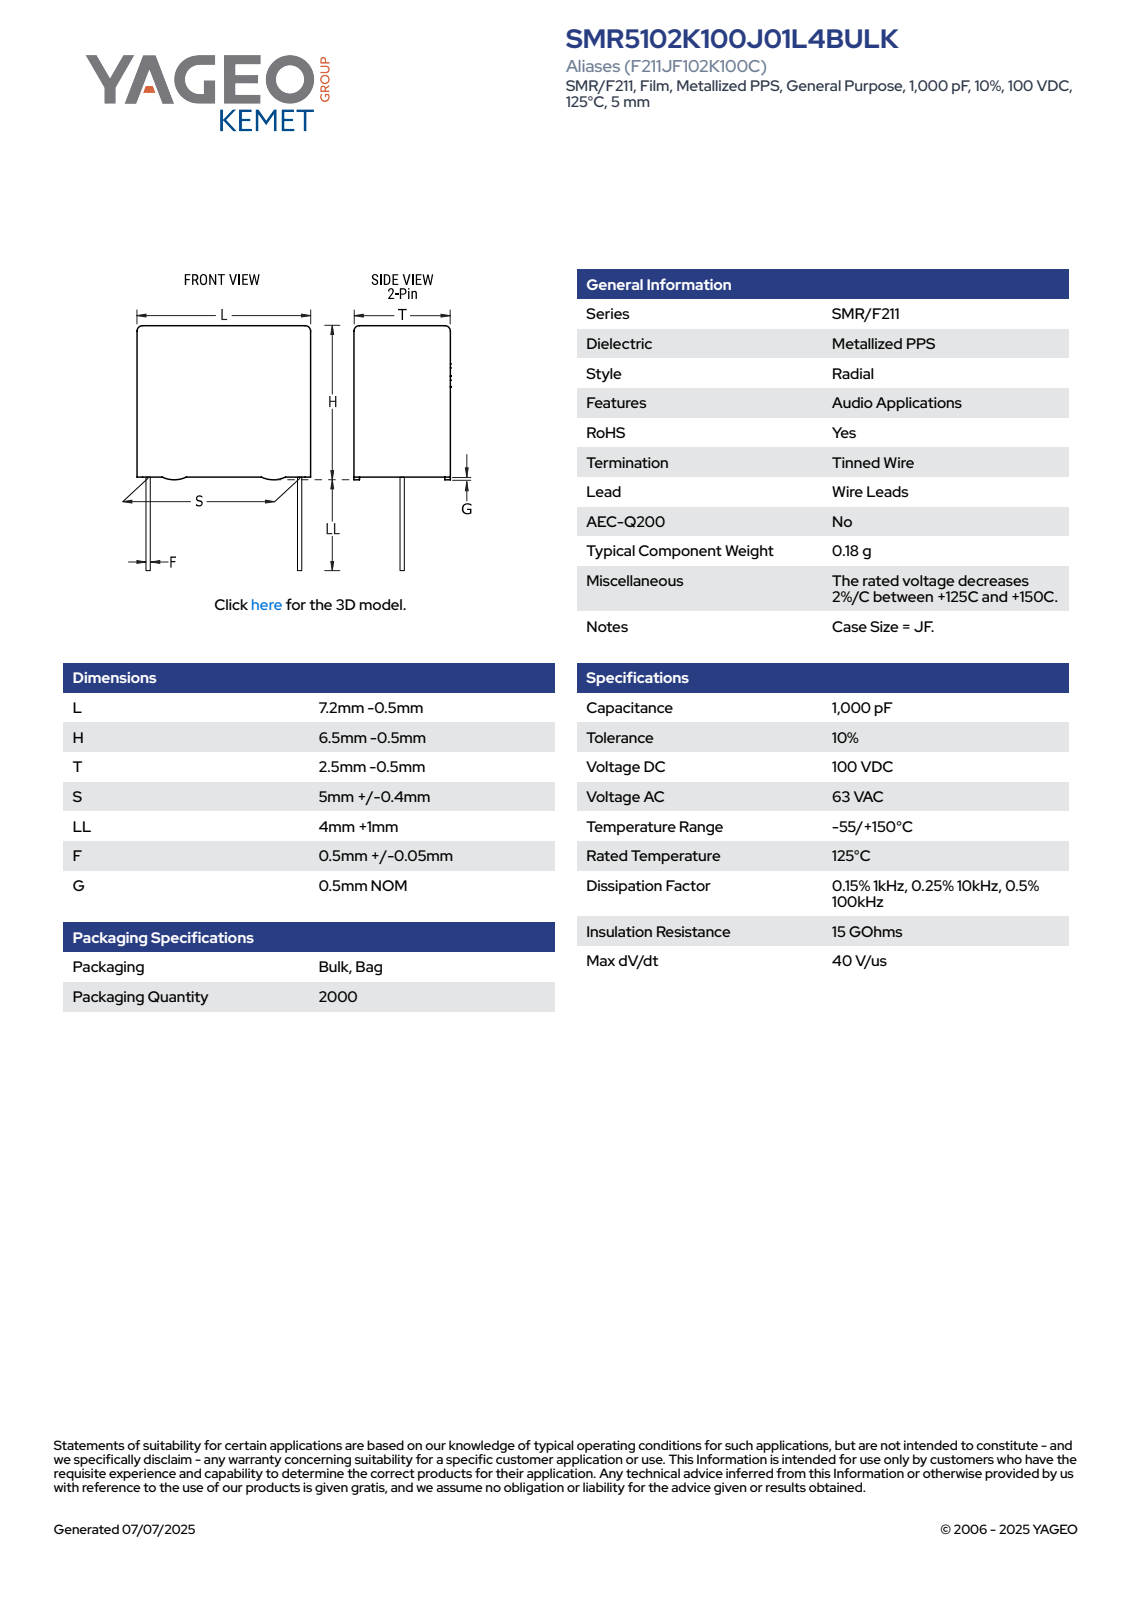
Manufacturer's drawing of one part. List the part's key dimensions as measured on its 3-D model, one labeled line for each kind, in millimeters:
Part name (STEP PRODUCT): CFR_RBG_7.2X6.5X2.5_L6.7H6T2S5LL5F0.55G0.5
STEP written by: SolidWorks 2021 (AUTOMOTIVE_DESIGN)
Units: millimetres
Bodies: 4 solids, 89 faces (81 planar, 8 cylindrical, 0 other)
Overall size (bounding box): 11 × 6.7 × 2
Volume: 76 mm³ · Surface area: 148 mm²
Round bosses / shafts (diameter × count): ⌀0.55 ×2
Partial cylindrical surfaces — rounded edges, fillets, slot ends (radius × count): R0.5 ×4
Main face-to-face distances: 2, 6.7, 5.5, 1.89, 1.78, 11, 5, 0.5, 6, 2.87
